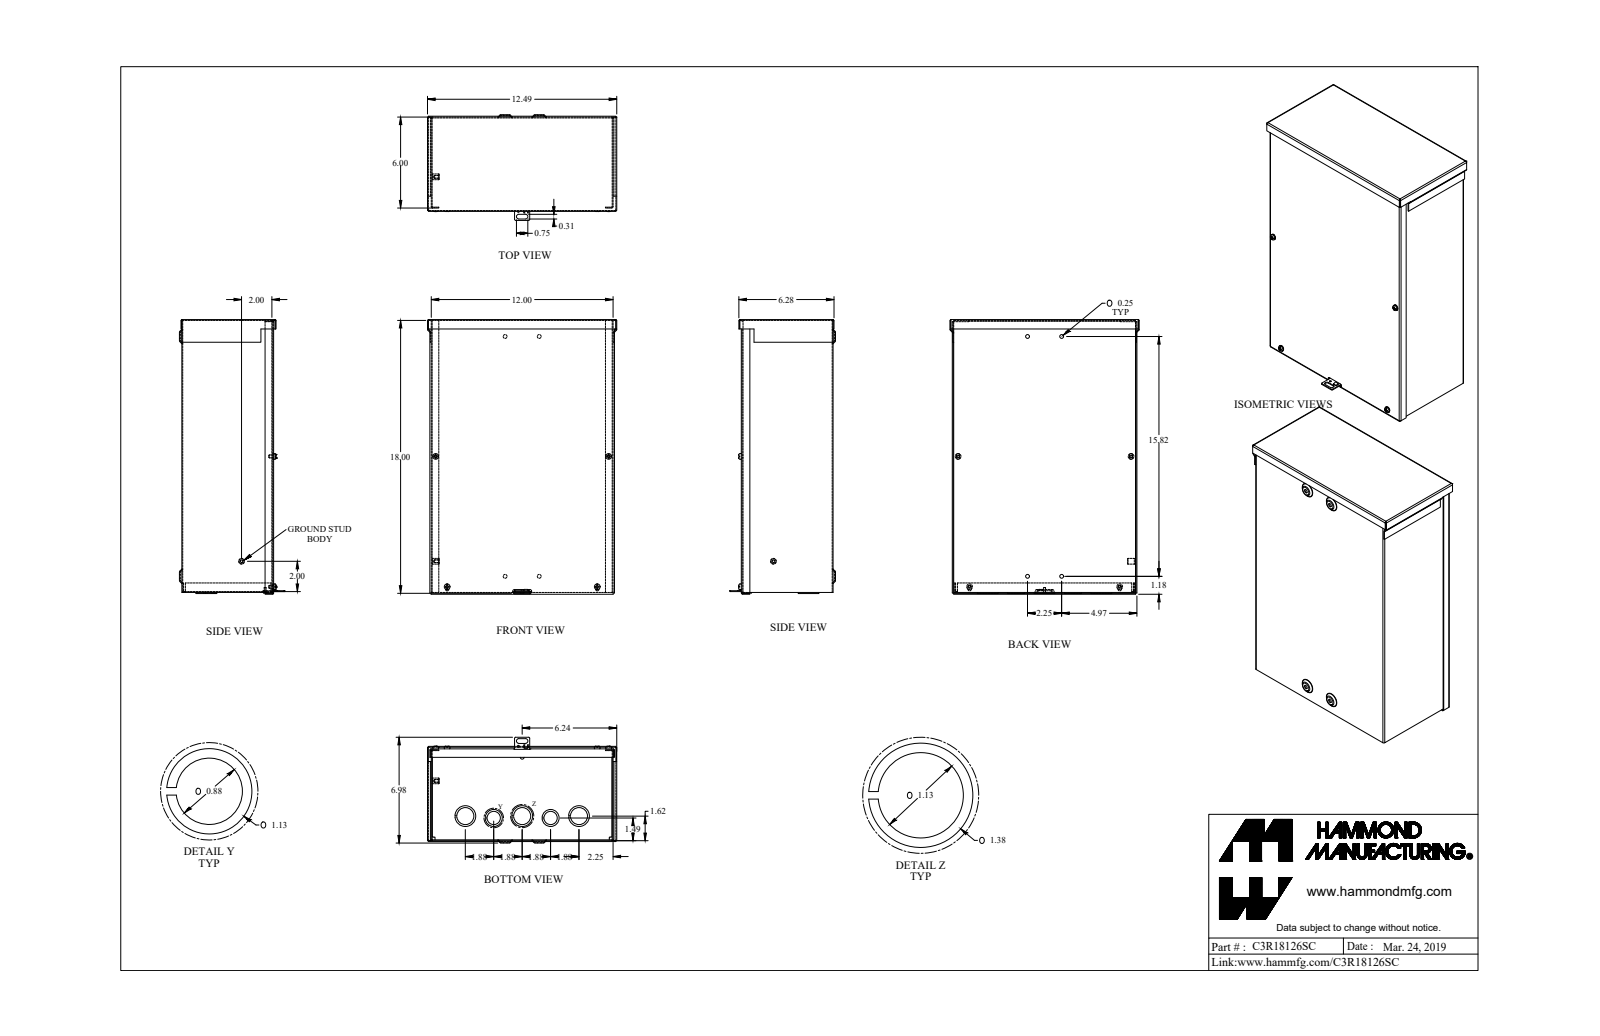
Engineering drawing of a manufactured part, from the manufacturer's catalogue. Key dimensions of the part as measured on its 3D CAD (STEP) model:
Part name (STEP PRODUCT): C3R18126SC_Default
STEP written by: SolidWorks 2019 (CONFIG_CONTROL_DESIGN)
Units: inches
Bodies: 11 solids, 429 faces (226 planar, 117 cylindrical, 86 other)
Overall size (bounding box): 18.12 × 12.489 × 6.977
Volume: 50.83 in³ · Surface area: 1 794 in²
Round holes (diameter × count): ⌀0.17 ×4, ⌀0.25 ×4, ⌀1.125 ×3, ⌀0.875 ×2, ⌀0.125 ×1, ⌀0.137 ×1, ⌀0.156 ×1
Round bosses / shafts (diameter × count): ⌀0.19 ×4, ⌀0.375 ×3, ⌀1.375 ×2, ⌀1.125 ×2, ⌀0.375 ×2, ⌀1.375 ×1, ⌀0.125 ×1
Partial cylindrical surfaces — rounded edges, fillets, slot ends (radius × count): R0.029 ×21, R0.086 ×21, R0.109 ×8, R0.125 ×8, R0.156 ×2
Main face-to-face distances: 0.057, 6, 5.943, 6.057, 11.943, 12, 0.057, 11.886, 17.886, 17.943
Hole centre spacings: 9.141, 10.451, 3.75, 1.879, 1.88, 2.25, 3.92, 5.396
